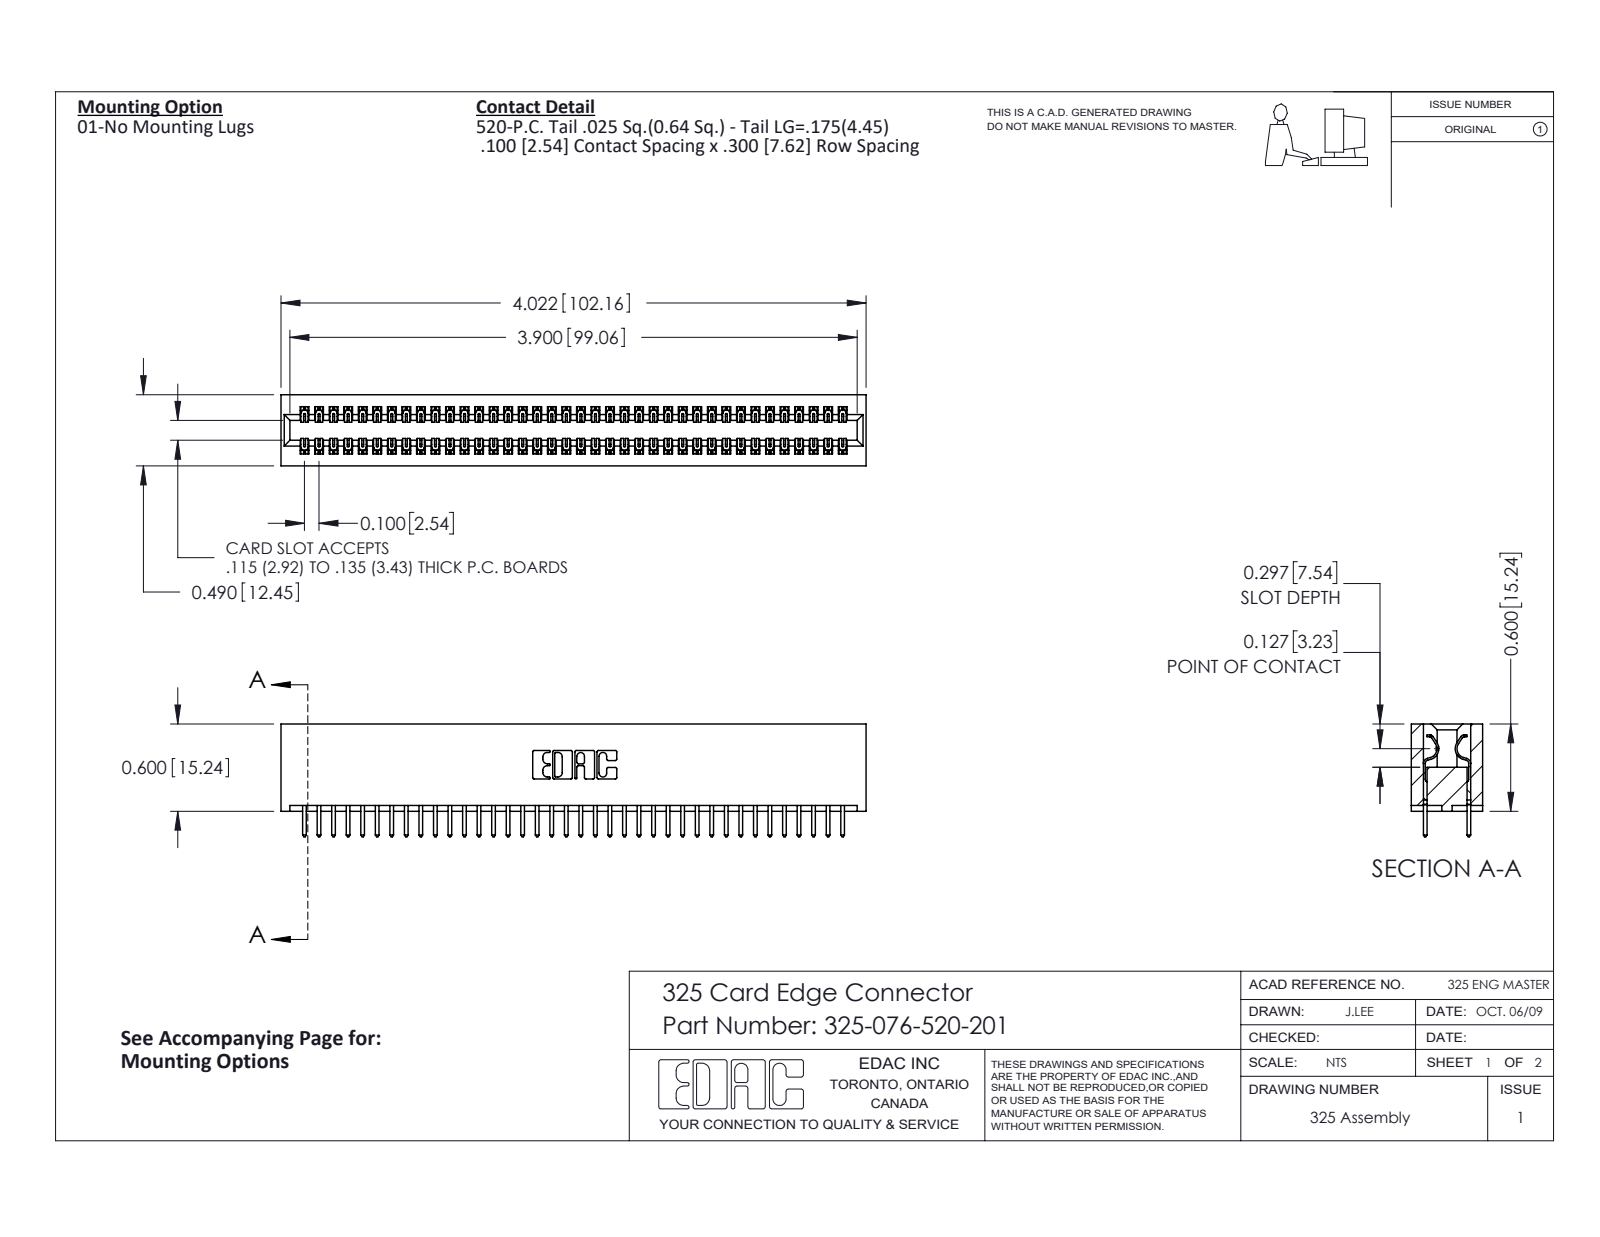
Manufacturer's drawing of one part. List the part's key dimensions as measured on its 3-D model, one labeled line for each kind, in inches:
Part name (STEP PRODUCT): 325 Part_Lugless; 325-076-520-201; 325-292-001_325-293-120
STEP written by: SolidWorks 2016 (CONFIG_CONTROL_DESIGN)
Units: inches
Bodies: 77 solids, 4058 faces (2802 planar, 1256 cylindrical, 0 other)
Overall size (bounding box): 4.022 × 0.775 × 0.49
Volume: 0.839 in³ · Surface area: 26.43 in²
Partial cylindrical surfaces — rounded edges, fillets, slot ends (radius × count): R0.006 ×114, R0.01 ×76, R0.01 ×22, R0.007 ×6, R0.031 ×6, R0.026 ×3, R0.014 ×2, R0.022 ×2
Main face-to-face distances: 0.083, 0.407, 0.3, 0.49, 0.107, 0.383, 0.025, 0.325, 0.275, 0.56
